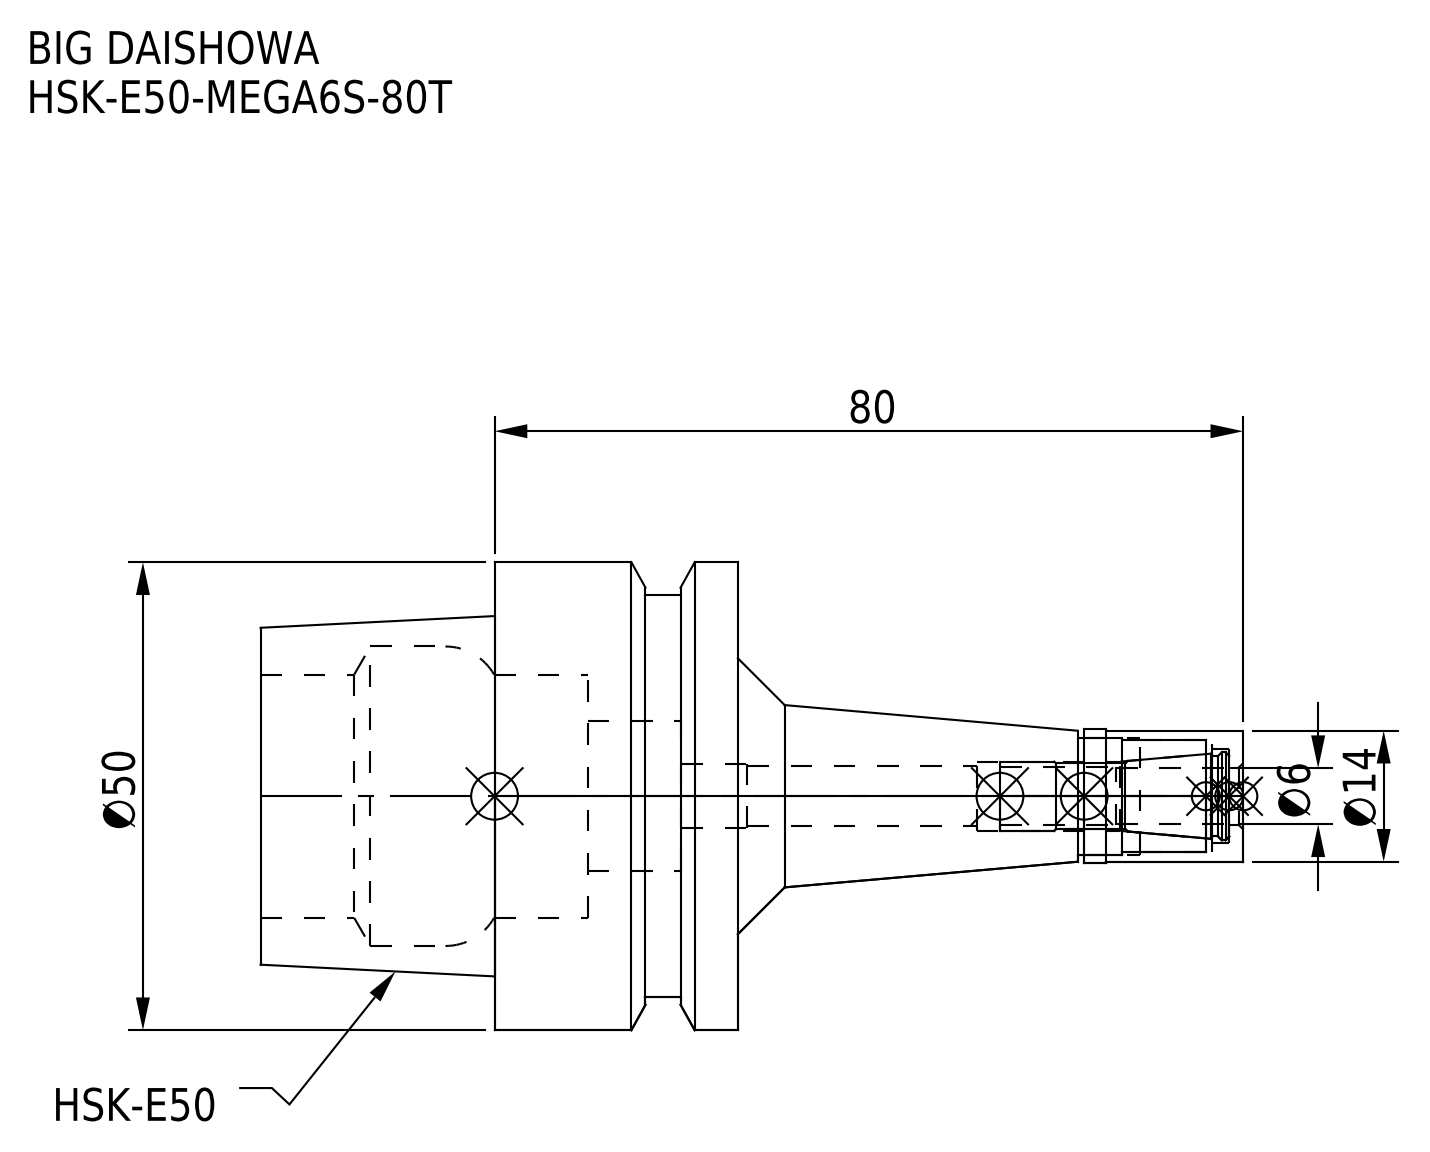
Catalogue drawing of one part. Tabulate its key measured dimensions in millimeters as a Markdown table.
| quantity | value |
| --- | --- |
| part name | MGN6S_1.stp; HSK-E50-MEGA6S-80T; DXF_TEMP_ASSY_ASM_4_ASM.stp; HSK-E50-MEGA6S-80T-060.stp (+3 more) |
| STEP written by | SolidWorks 2019 (CONFIG_CONTROL_DESIGN) |
| units | millimeters |
| bodies | 2 solids, 74 faces (18 planar, 38 cylindrical, 18 other) |
| overall size | 105 × 50 × 50 |
| volume | 61 372 mm³ |
| surface area | 20 187 mm² |
| round holes (diameter × count) | 6.1 × 1, 6.4 × 1, 6.8 × 1, 7.4 × 1, 10 × 1, 12 × 1, 12.5 × 1, 16 × 1, 26 × 1, 32 × 1 |
| round bosses / shafts (diameter × count) | 50 × 1, 43 × 1, 14.3 × 1, 14 × 1 |
| main face-to-face distances | 26, 51, 25, 16.05, 9.95, 34.95, 6.05, 10, 19.95, 44.95 |
